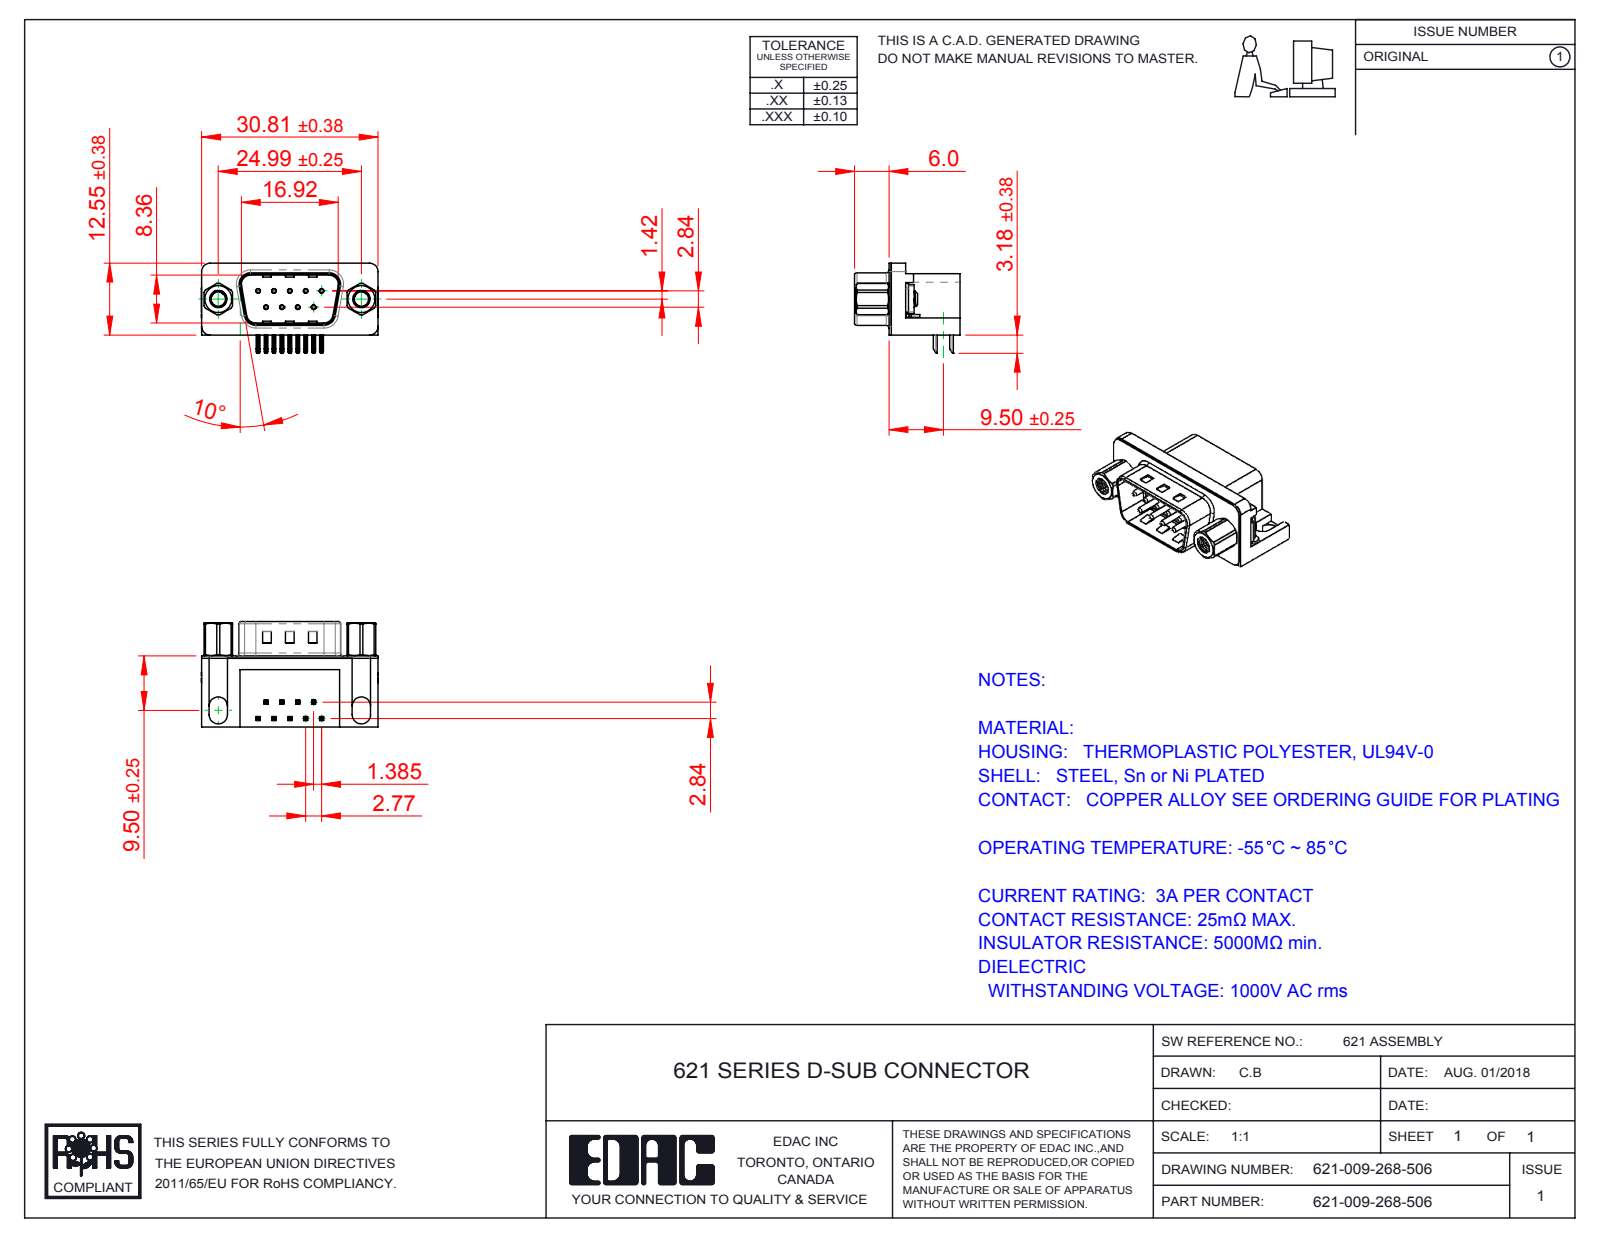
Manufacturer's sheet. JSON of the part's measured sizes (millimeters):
{"part_name": "621 M3 Hex Standoff 5; 621 Contact Bottom; 621 Non Board Mount; 621 Contact Top (+4 more)", "step_written_by": "SolidWorks 2016 (CONFIG_CONTROL_DESIGN)", "units": "millimeters", "bodies": {"solids": 17, "faces": 1133, "planar": 593, "cylindrical": 407, "other": 133}, "overall_size": [30.89, 18.4, 15.73], "volume_mm3": 3449, "surface_area_mm2": 4780, "round_holes": [[0.35, 9], [0.8, 9], [2.5, 2], [4, 2], [4.8, 2], [5, 2]], "round_bosses_or_shafts": [[0.75, 9], [4.9, 2], [4.75, 2], [3.9, 2], [3, 2]], "partial_cylinders_radius": [[0.25, 44], [0.12, 18], [1, 16], [0.5, 9], [1.5, 8], [1.6, 8], [0.9, 4], [2, 4]], "face_to_face_distances": [0.4, 12, 12.4, 10.35, 9.5, 2.5, 2.9, 2.1, 0.35, 10.7], "hole_center_spacings": [3.16, 2.77, 5.54, 5.03, 5.04, 8.31, 7.48, 7.49]}
